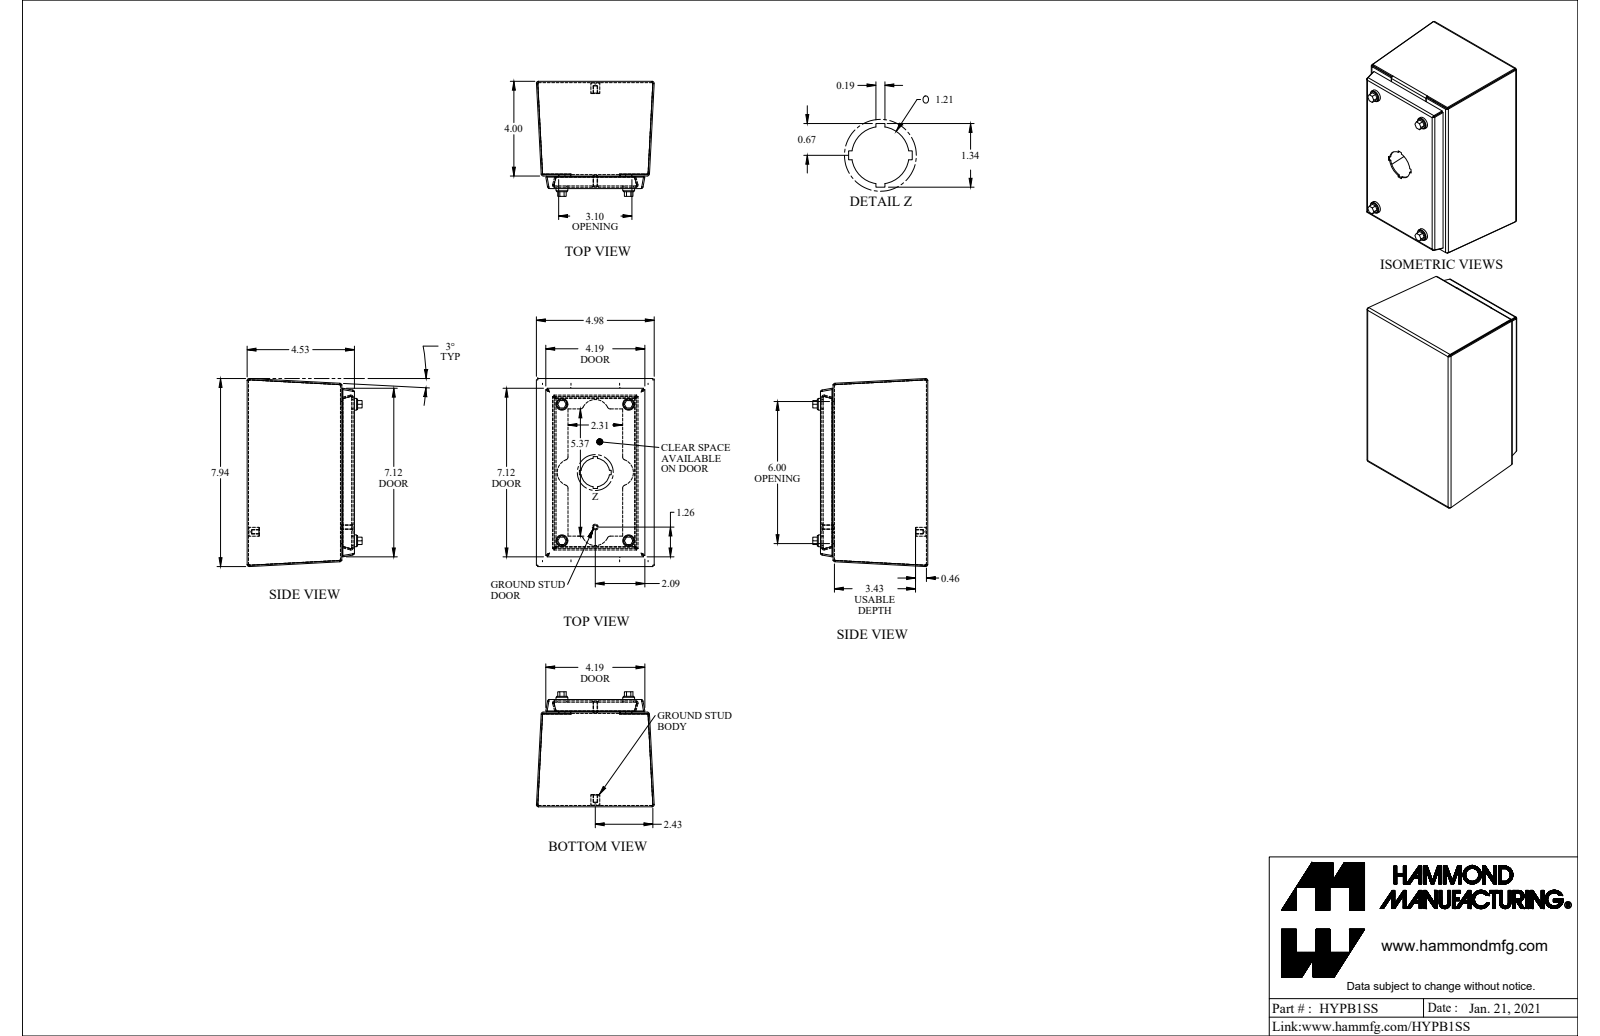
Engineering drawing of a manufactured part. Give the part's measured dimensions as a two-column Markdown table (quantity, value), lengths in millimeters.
| quantity | value |
| --- | --- |
| part name | HYPB1SS |
| STEP written by | SolidWorks 2021 (AUTOMOTIVE_DESIGN) |
| units | millimeters |
| bodies | 22 solids, 467 faces (308 planar, 136 cylindrical, 23 other) |
| overall size | 201.7 × 126.4 × 123.4 |
| volume | 241 400 mm³ |
| surface area | 304 800 mm² |
| round holes (diameter × count) | 1.7 × 4, 6 × 4, 6.1 × 4, 6.1 × 4, 6.4 × 4, 6.4 × 4, 10.2 × 4, 4 × 1, 30.7 × 1 |
| round bosses / shafts (diameter × count) | 9.5 × 5, 4.8 × 5, 12.7 × 4, 11.4 × 4, 10.3 × 4, 8 × 4, 6.4 × 1 |
| partial cylindrical surfaces (radius × count) | 0.7 × 16, 2.2 × 16, 3.2 × 12, 1.4 × 4, 1.9 × 4, 12.7 × 4, 14.6 × 4 |
| main face-to-face distances | 1.4, 112.2, 113.7, 100.2, 1.4, 115.1, 113.7, 12.1, 101.6, 13.5 |
| hole center spacings | 163, 146.5, 71.6, 146.5, 81.5, 71.6, 163, 141.4 |
